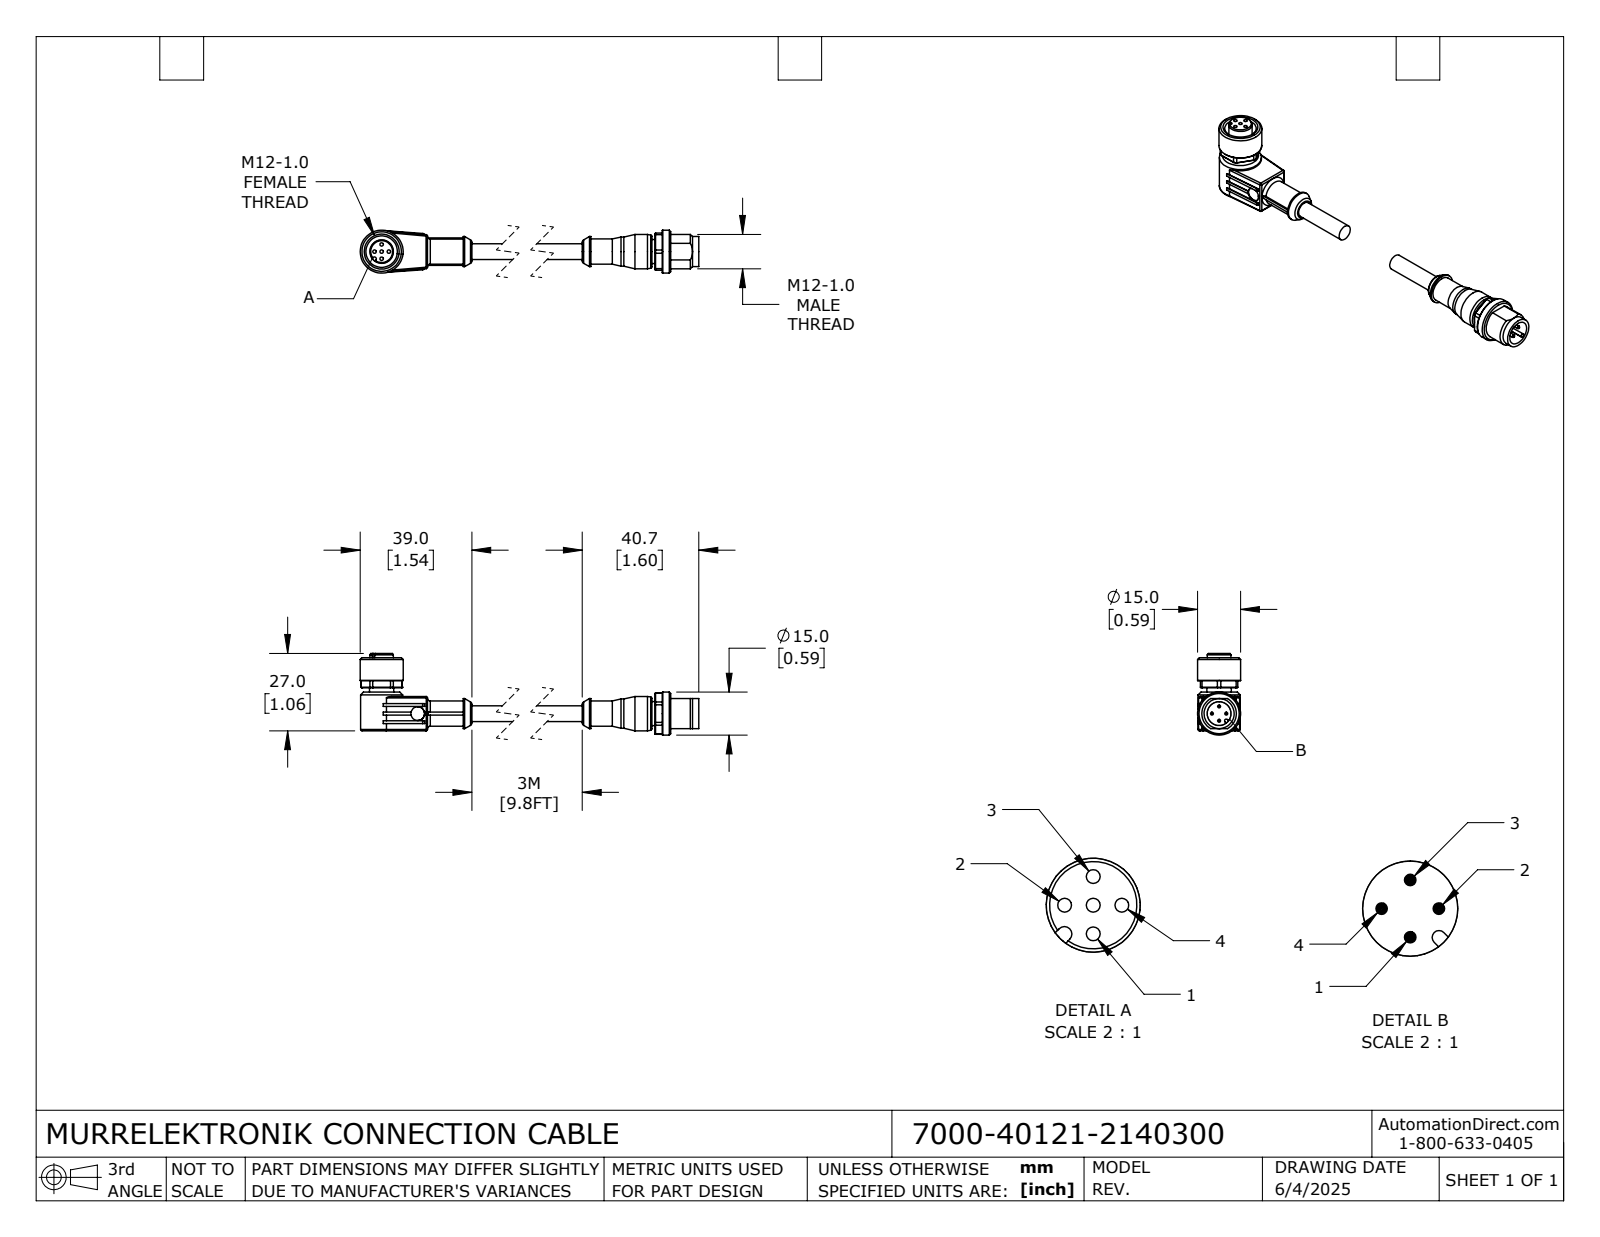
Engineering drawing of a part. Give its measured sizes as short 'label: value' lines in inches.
name: 7000-40121-2140300_MALE; 7000-40121-2140300; 7000-40121-2140300_FEMALE 90
written by: SolidWorks 2024 (CONFIG_CONTROL_DESIGN)
unit: in
bodies: 2 solids, 248 faces (91 planar, 95 cylindrical, 62 other)
size: 5.697 × 1.122 × 0.591
volume: 0.657 in³; area: 9.438 in²
holes: 5× ⌀0.047, 1× ⌀0.189, 1× ⌀0.327, 1× ⌀0.433
bosses: 4× ⌀0.039, 2× ⌀0.591, 1× ⌀0.579, 1× ⌀0.472, 1× ⌀0.413, 1× ⌀0.402, 1× ⌀0.346, 1× ⌀0.335
rounds: 8× R0.02, 2× R0.039, 2× R0.283, 1× R0.024, 1× R0.026
face distances: 0.472, 0.118, 0.059, 0.531, 0.591, 0.217, 0.512, 0.03, 0.443, 0.413
hole spacings: 0.098, 0.139, 0.197
